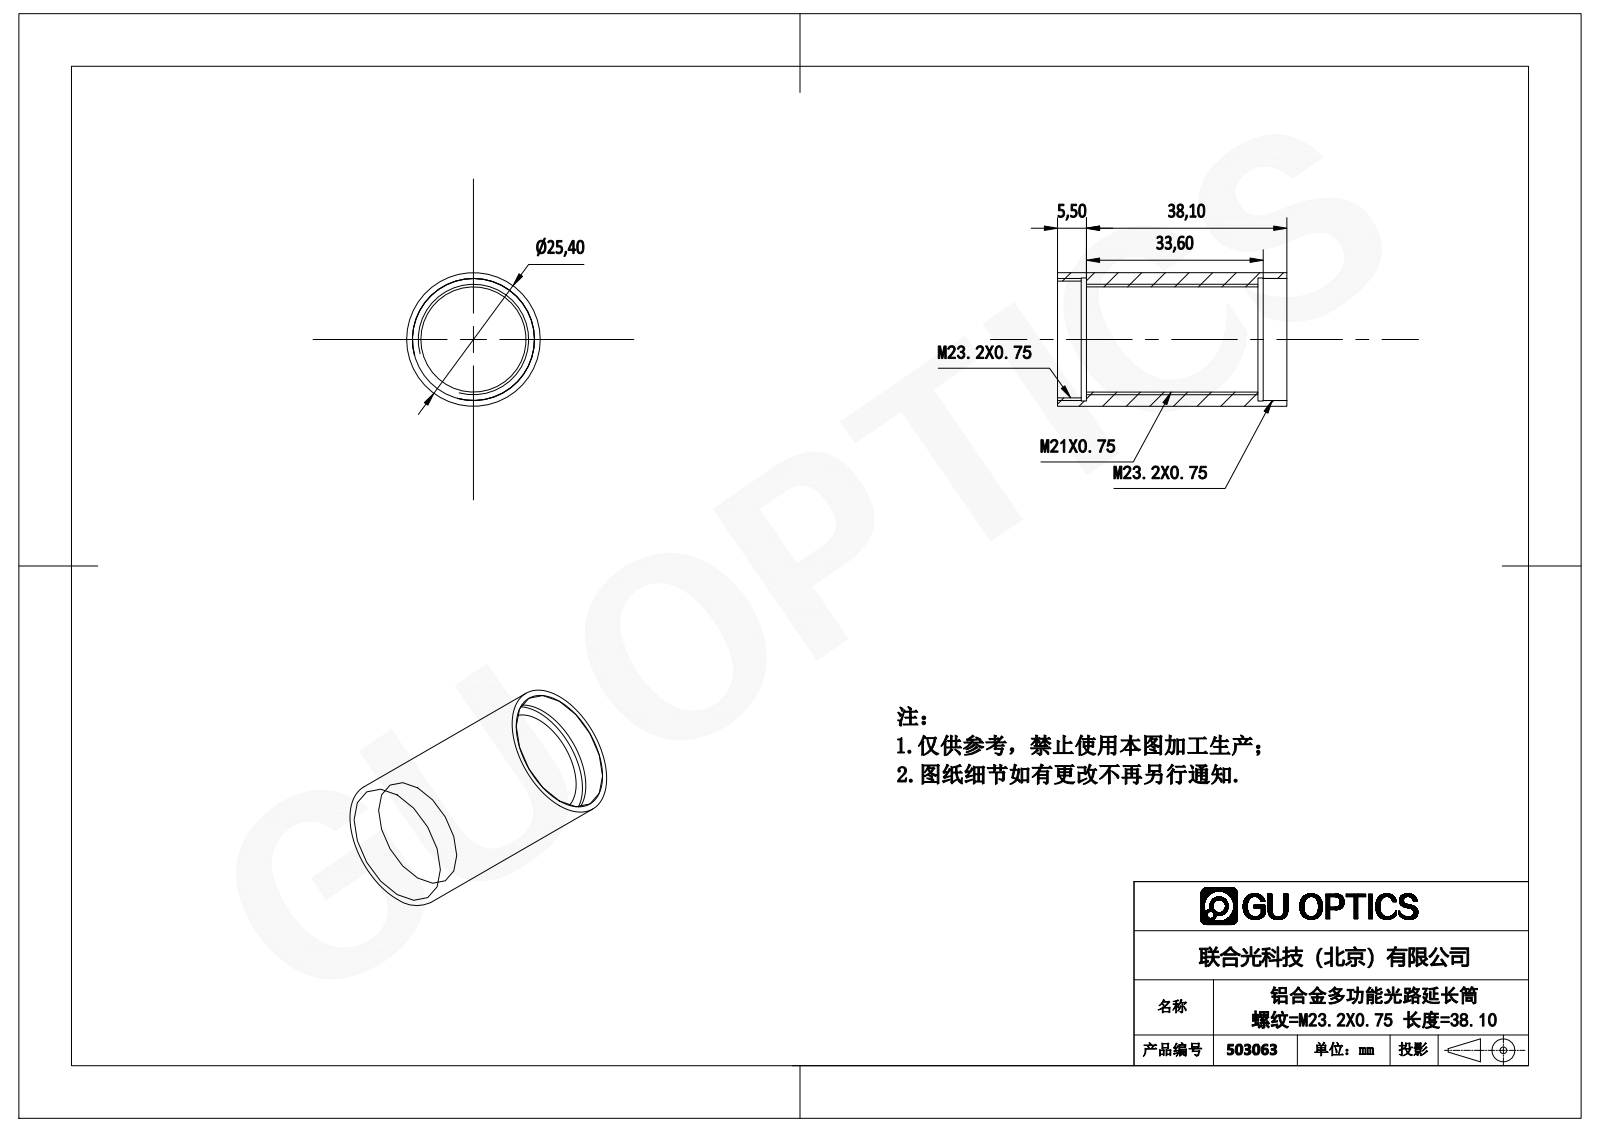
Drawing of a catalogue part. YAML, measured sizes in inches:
part_name: "503063"
step_written_by: "SolidWorks 2016 (AUTOMOTIVE_DESIGN)"
units: inches
bodies: {solids: 1, faces: 18, planar: 6, cylindrical: 12, other: 0}
overall_size: [1.717, 1, 1]
volume: 0.448
surface_area: 10.54
round_holes:
  - {diameter: 0.787, count: 1}
  - {diameter: 0.874, count: 1}
  - {diameter: 0.913, count: 1}
  - {diameter: 0.921, count: 1}
round_bosses_or_shafts:
  - {diameter: 1, count: 1}
face_to_face_distances: [0.217, 1.5, 1.283, 1.717, 0.177, 1.539, 0.039, 1.323, 1.362]
